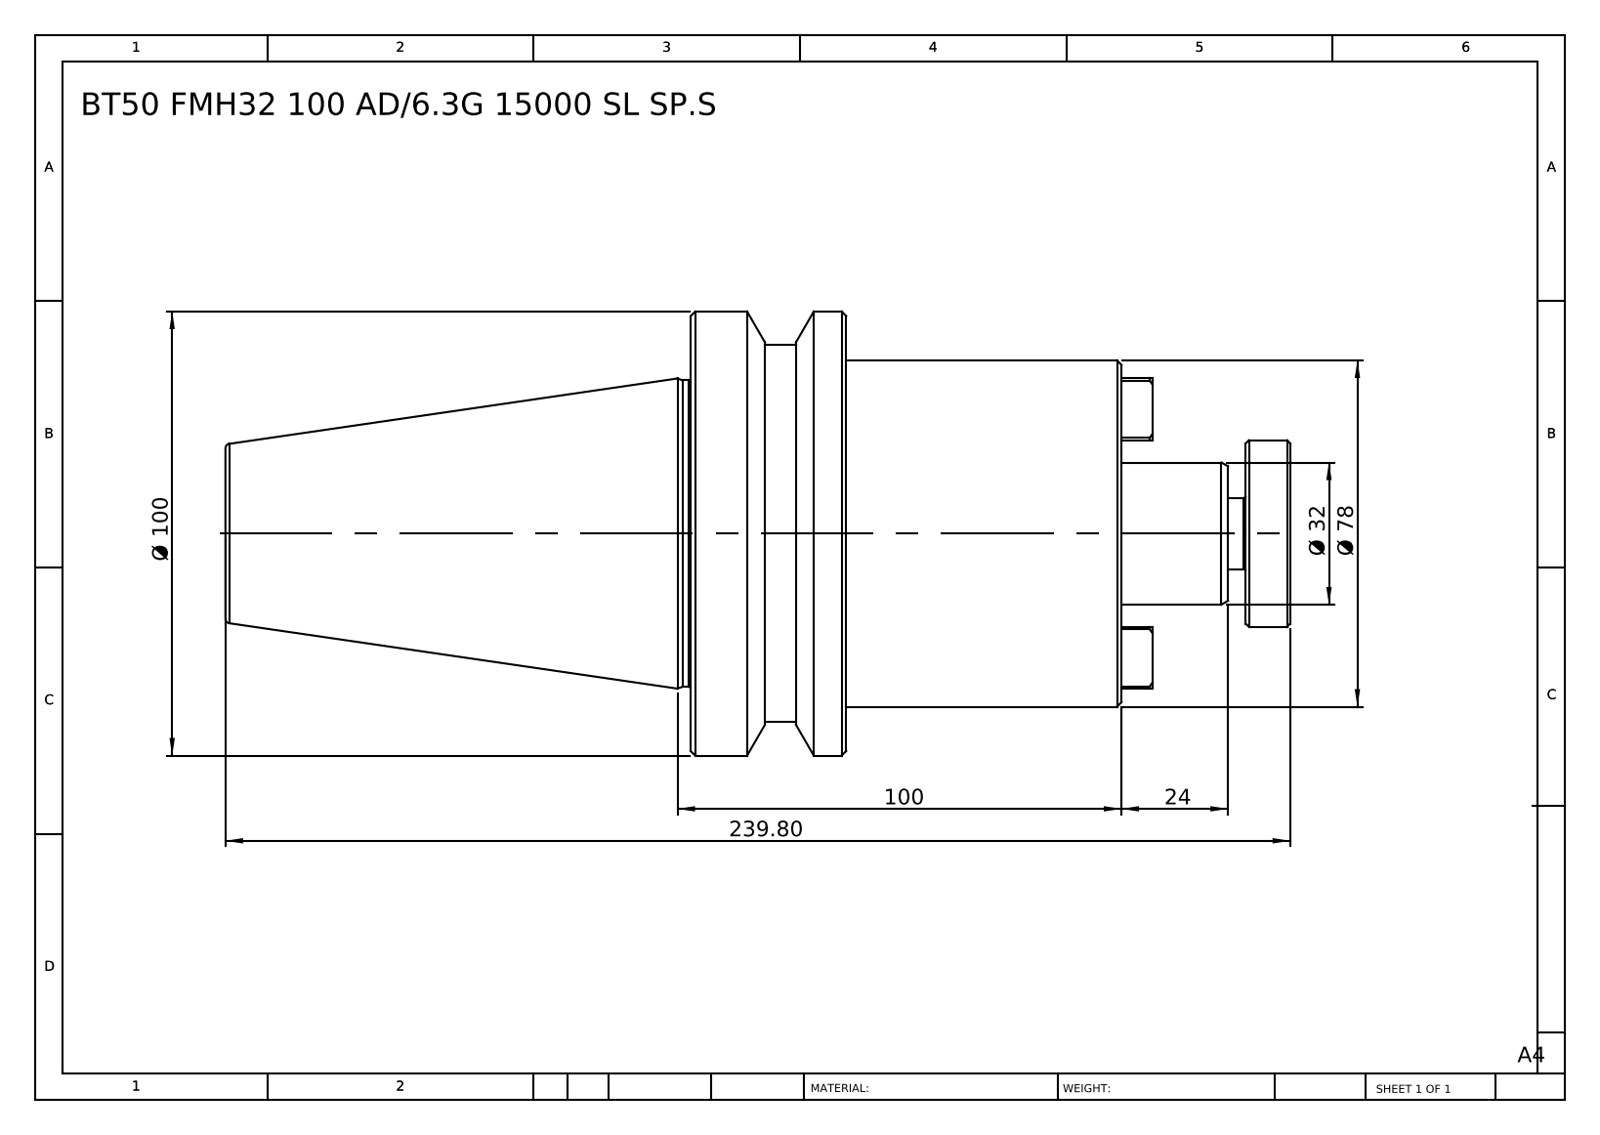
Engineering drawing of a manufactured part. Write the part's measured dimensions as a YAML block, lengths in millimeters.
part_name: "BT50 FMH32 100 AD-6.3G 15000 SL SP.S"
step_written_by: "SolidWorks 2014 (CONFIG_CONTROL_DESIGN)"
units: millimeters
bodies: {solids: 1, faces: 77, planar: 35, cylindrical: 16, other: 26}
overall_size: [239.8, 100, 100]
volume: 842821
surface_area: 66290
round_bosses_or_shafts:
  - {diameter: 100, count: 1}
  - {diameter: 85, count: 1}
  - {diameter: 78, count: 1}
  - {diameter: 69, count: 1}
  - {diameter: 42, count: 1}
  - {diameter: 32, count: 1}
  - {diameter: 16, count: 1}
face_to_face_distances: [97, 62, 35, 38, 100, 135, 239.8, 201.8, 139.8, 104.8]
